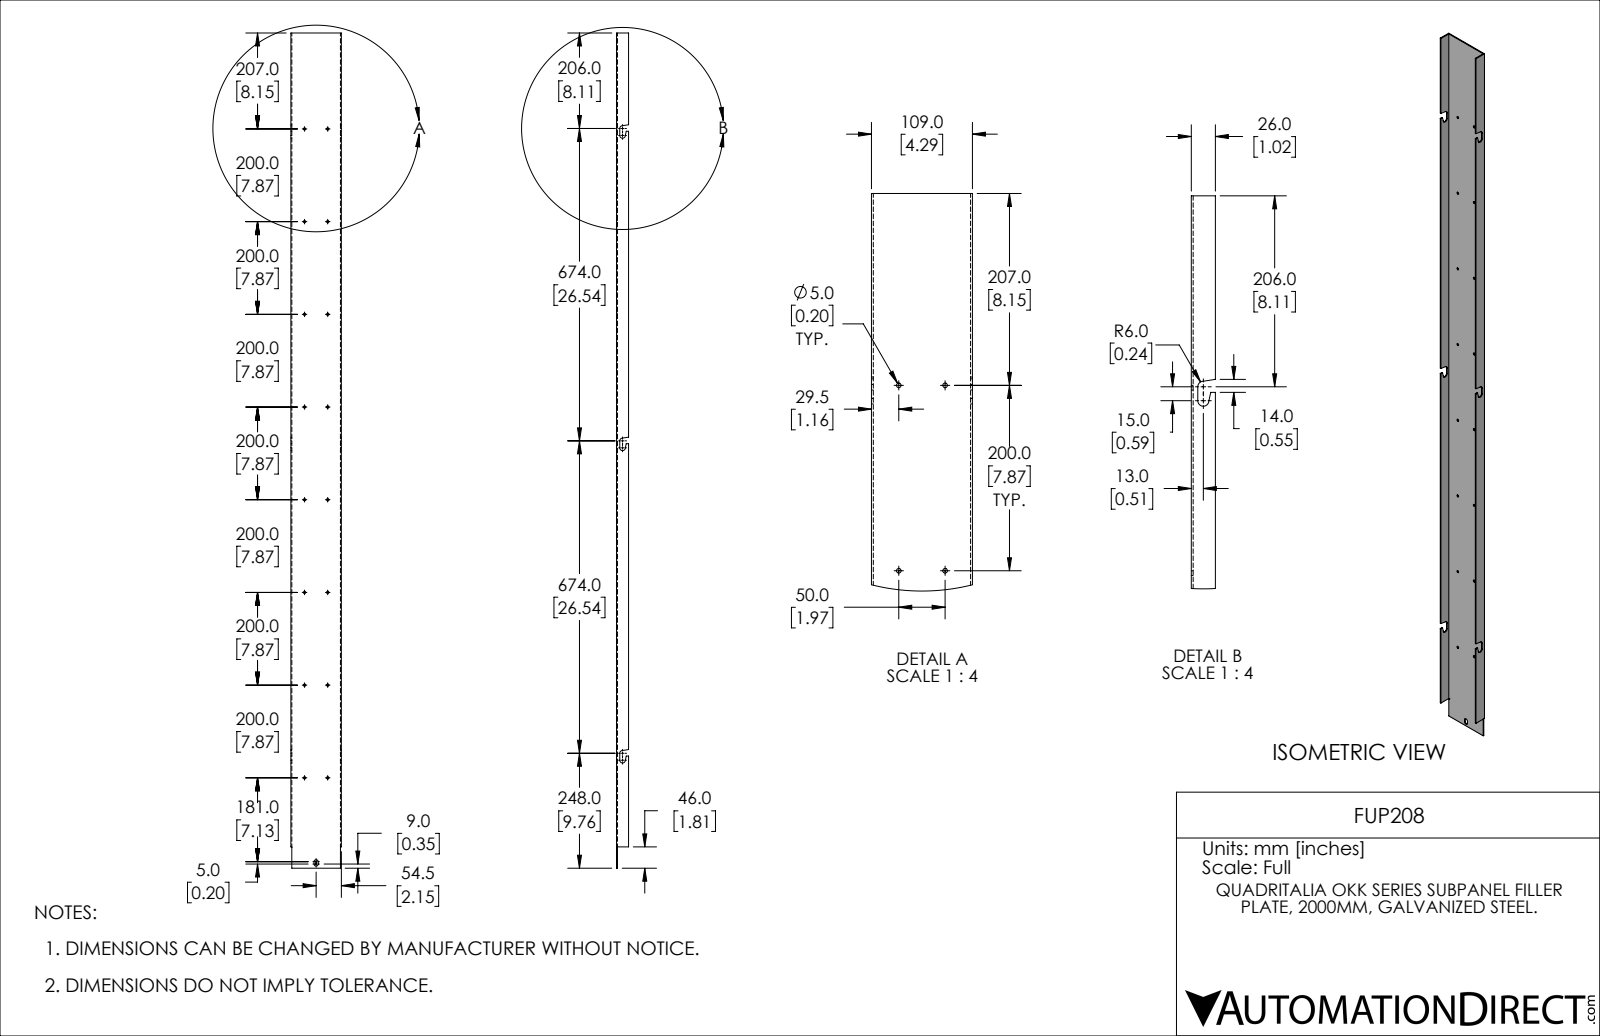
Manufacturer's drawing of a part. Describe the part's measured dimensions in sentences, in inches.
The part is named "FUP208". Its 3-D file was written by "SolidWorks 2021 (CONFIG_CONTROL_DESIGN)". It is 1 solid with 80 faces: 50 planar, 30 cylindrical and 0 other. Overall it measures 70.945 by 4.291 by 1.024 inches. Its volume is 33.89 cubic inches and its surface area 874.8 square inches. Round holes: 16 of diameter 0.197. Partial cylindrical surfaces (rounded edges, fillets, slot ends): 6 of radius 0.236, 2 of radius 0.177. The main face-to-face distances are 0.079, 4.213, 4.291, 4.134, 1.024, 0.945, 70.945, 0.276, 0.197, 0.748. The hole center spacings are 7.874, 8.117, 15.748, 15.87, 23.622, 23.704, 1.969, 31.496.
